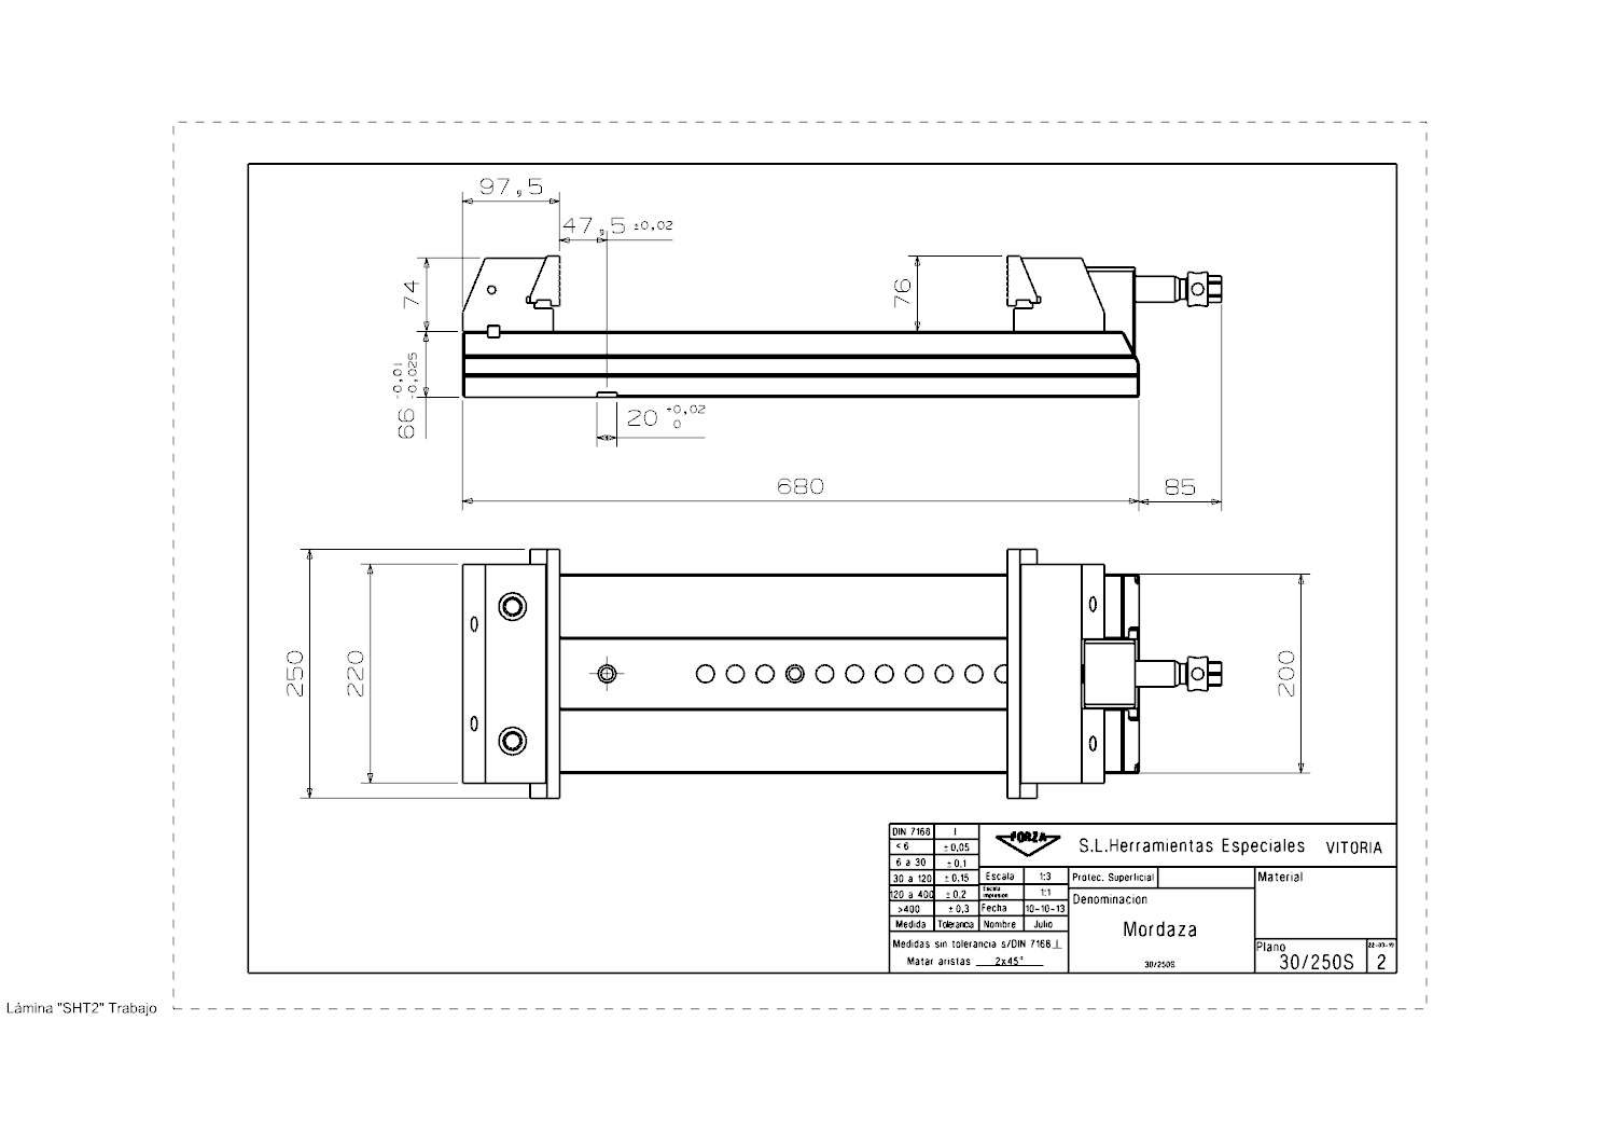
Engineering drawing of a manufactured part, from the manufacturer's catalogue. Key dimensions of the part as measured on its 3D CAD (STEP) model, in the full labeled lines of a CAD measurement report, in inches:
Part name (STEP PRODUCT): 30_250S_Mordaza
STEP written by: SIEMENS PLM Software NX 11.0 (AUTOMOTIVE_DESIGN)
Units: inches
Bodies: 13 solids, 632 faces (466 planar, 103 cylindrical, 63 other)
Overall size (bounding box): 30.039 × 9.843 × 5.591
Volume: 605.7 in³ · Surface area: 1 346 in²
Round holes (diameter × count): ⌀0.748 ×5, ⌀0.204 ×4, ⌀0.374 ×4, ⌀0.591 ×4, ⌀0.709 ×4, ⌀0.236 ×3, ⌀0.346 ×3, ⌀0.417 ×3, ⌀0.487 ×3, ⌀0.512 ×3, ⌀0.256 ×2, ⌀0.275 ×2
Round bosses / shafts (diameter × count): ⌀1.339 ×1, ⌀1.331 ×1, ⌀1.024 ×1, ⌀0.787 ×1, ⌀0.65 ×1
Partial cylindrical surfaces — rounded edges, fillets, slot ends (radius × count): R0.394 ×8, R0.256 ×2, R0.354 ×1, R0.413 ×1, R0.492 ×1, R0.522 ×1
Main face-to-face distances: 2.598, 1.327, 1.272, 0.059, 1.268, 2.539, 5.709, 0.394, 2.559, 7.874
Hole centre spacings: 0.787, 0.866, 0.996, 1.075, 1.115, 1.181, 1.393, 1.824
